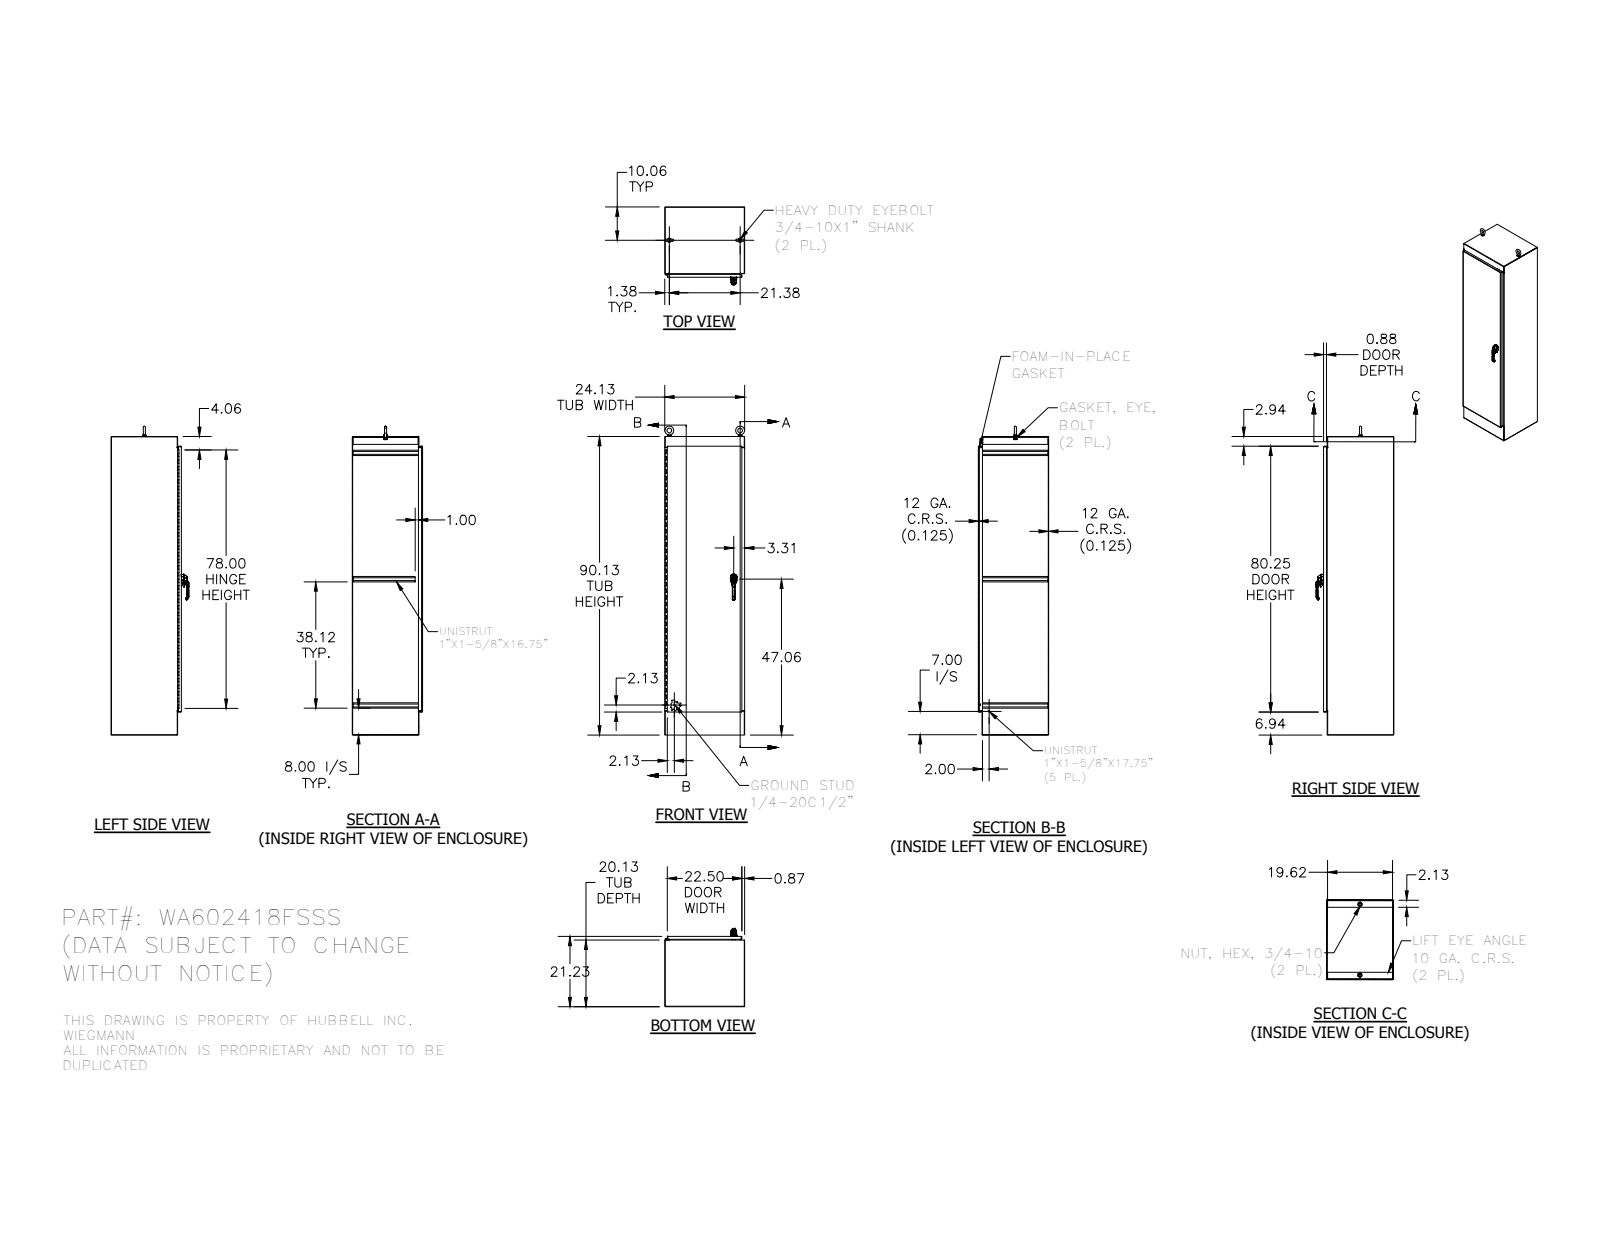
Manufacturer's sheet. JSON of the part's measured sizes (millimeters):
{"part_name": "WA9024FSFB; WA9020FSLS; WA9020FSRS; WA2420FSBTM-10GA (+8 more)", "step_written_by": "Autodesk Inventor 2014 (AUTOMOTIVE_DESIGN)", "units": "millimeters", "bodies": {"solids": 47, "faces": 2834, "planar": 1207, "cylindrical": 980, "other": 647}, "overall_size": [2368.49, 612.77, 596.35], "volume_mm3": 20570000, "surface_area_mm2": 13260000, "round_holes": [[7.02, 8], [9.52, 8], [5.08, 4], [5.4, 3], [7.11, 3], [8, 2], [10.2, 2], [10.33, 2], [10.5, 2], [16.31, 2], [20.64, 2], [3.1, 1]], "round_bosses_or_shafts": [[31.75, 2], [28.45, 2], [19.05, 2], [13.5, 2], [13.37, 2], [11.05, 2], [8.56, 2], [6.35, 2]], "partial_cylinders_radius": [[0.5, 170], [0.3, 101], [0.47, 21], [0.25, 16], [3.17, 16], [0.79, 14], [2, 14], [3.97, 14]], "face_to_face_distances": [3.18, 609.6, 3.17, 606.42, 612.78, 532.88, 536.06, 539.23, 536.05, 2286], "hole_center_spacings": [220.13, 660.4, 440.27, 880.53, 9.66, 9.7, 9.71, 19.36]}
